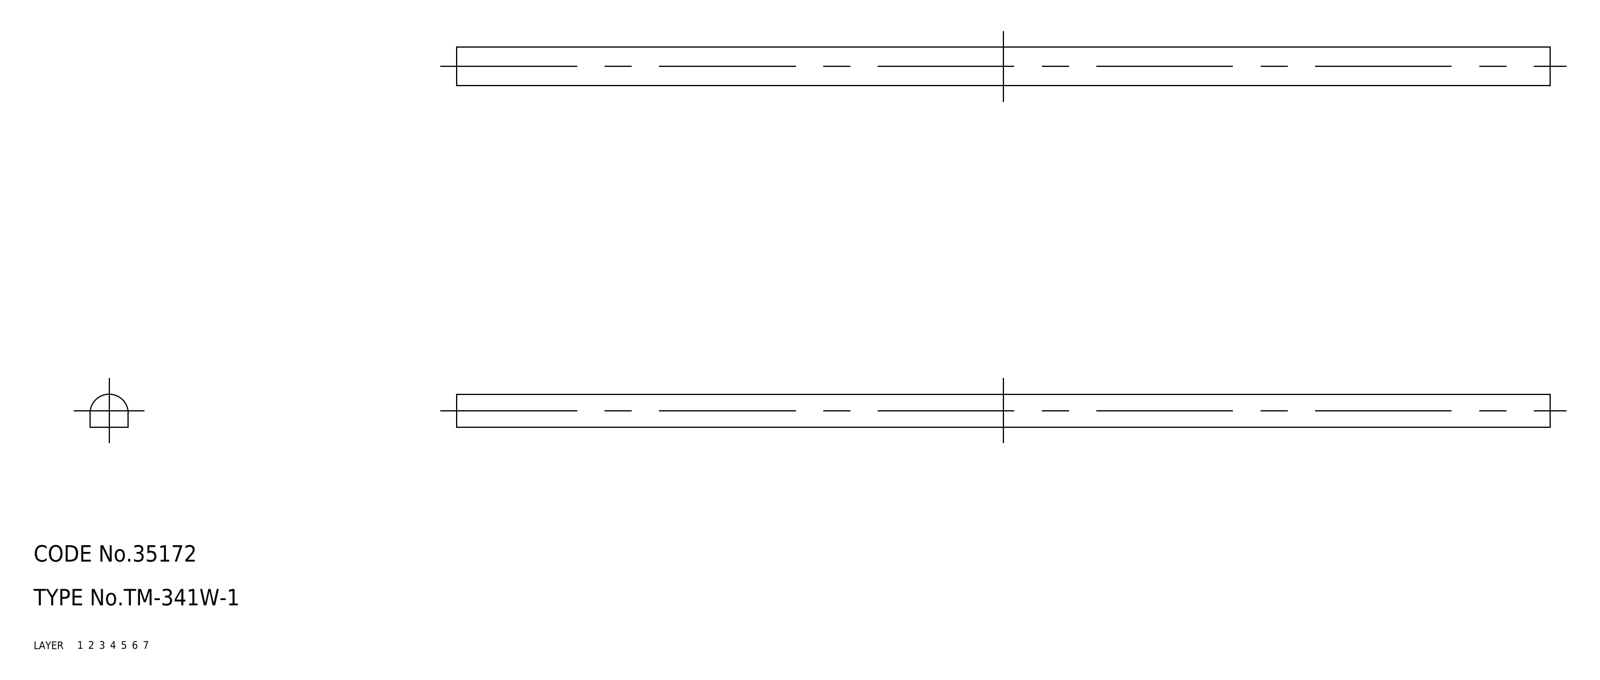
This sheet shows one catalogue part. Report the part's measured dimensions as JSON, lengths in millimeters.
{"part_name": "rubber foam; TM_341W_1", "step_written_by": "SolidWorks 2015 (AUTOMOTIVE_DESIGN)", "units": "millimeters", "bodies": {"solids": 1, "faces": 6, "planar": 5, "cylindrical": 1, "other": 0}, "overall_size": [200, 7, 6], "volume_mm3": 7348, "surface_area_mm2": 4673, "partial_cylinders_radius": [[3.5, 1]], "face_to_face_distances": [7, 200]}
